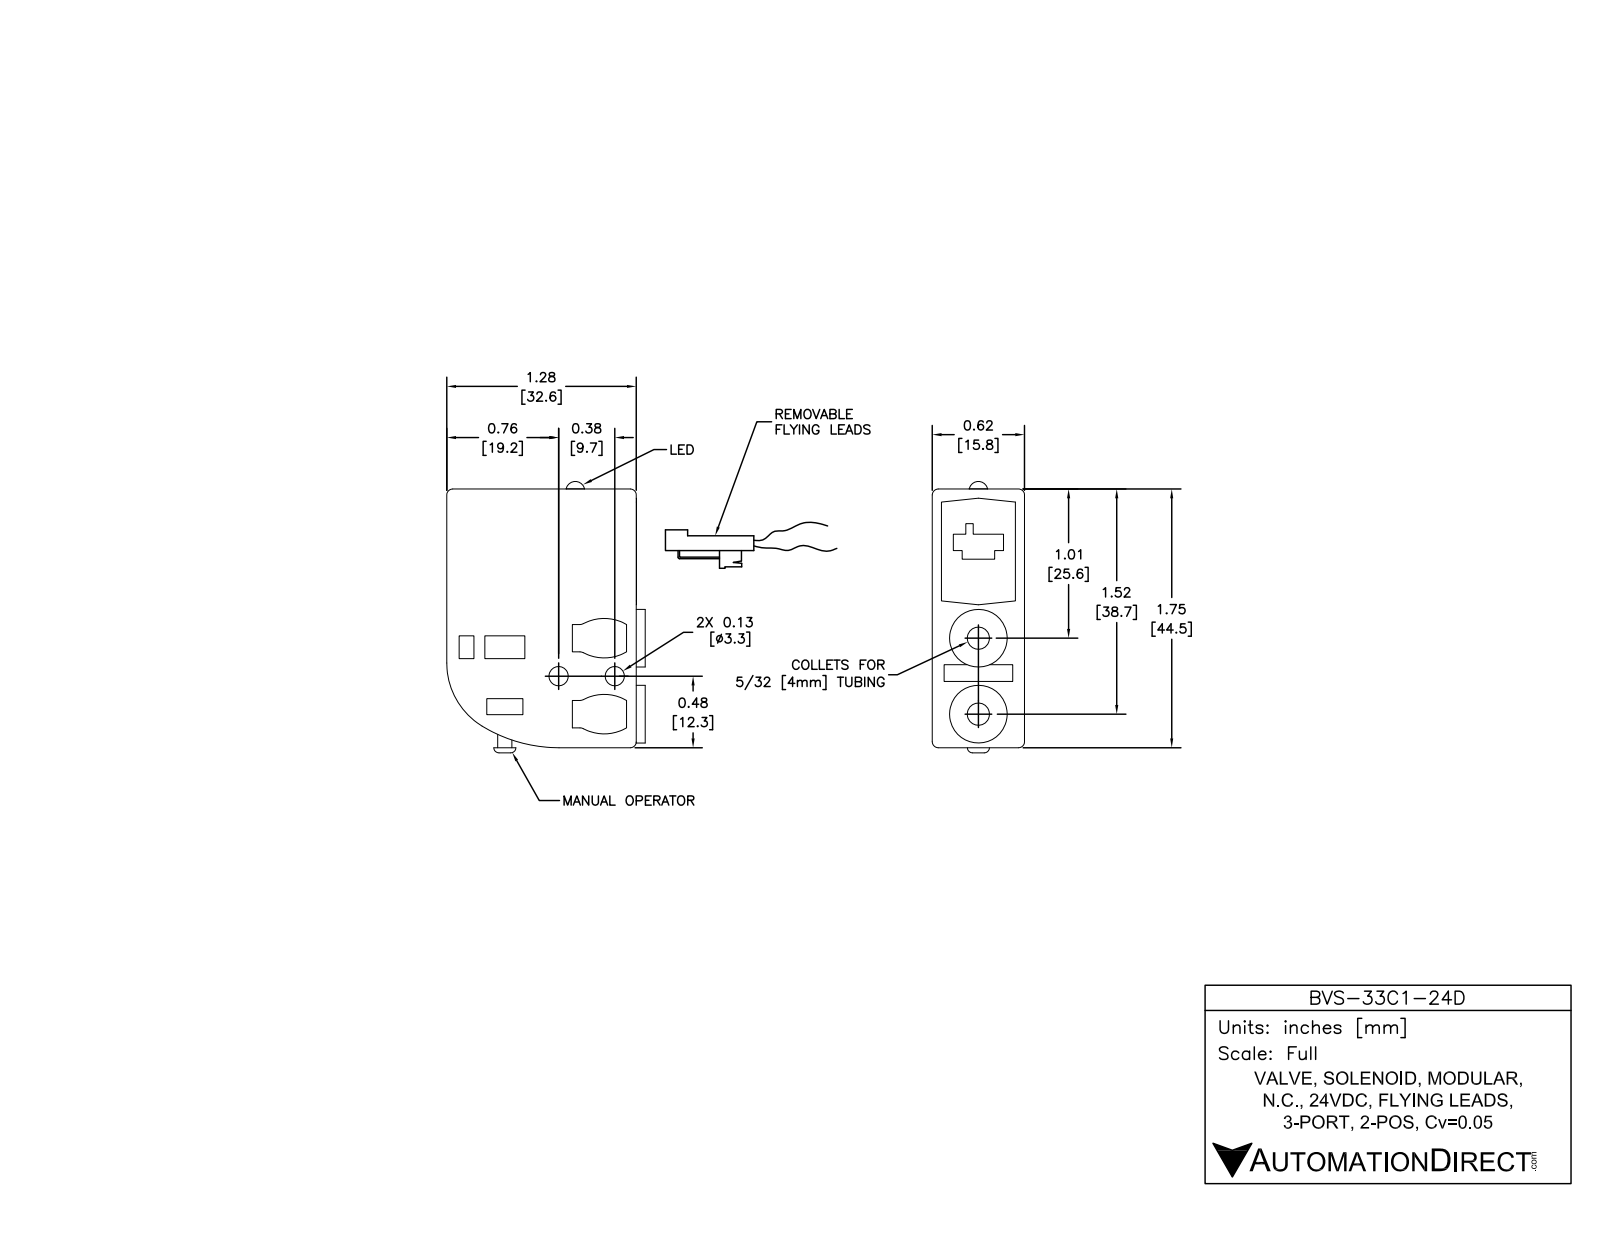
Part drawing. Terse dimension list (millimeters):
name: BVS-33C1-24D
written by: SolidWorks 2013 (AUTOMOTIVE_DESIGN)
unit: mm
bodies: 1 solid, 158 faces (93 planar, 52 cylindrical, 13 other)
size: 46.6 × 34.2 × 15.8
volume: 20 420 mm³; area: 6 561 mm²
holes: 2× ⌀3.3, 2× ⌀3.8, 2× ⌀6.5, 1× ⌀1.2
bosses: 2× ⌀9.9, 1× ⌀3.1, 1× ⌀2.4
rounds: 11× R1, 4× R1.3, 4× R7.6, 1× R12.7, 1× R25.4
face distances: 15.8, 2.5, 13.3, 32.7, 32.7, 44.5, 10.8, 1.5, 1.5, 34.2
hole spacings: 1.5, 9.7, 11.5, 13.1
